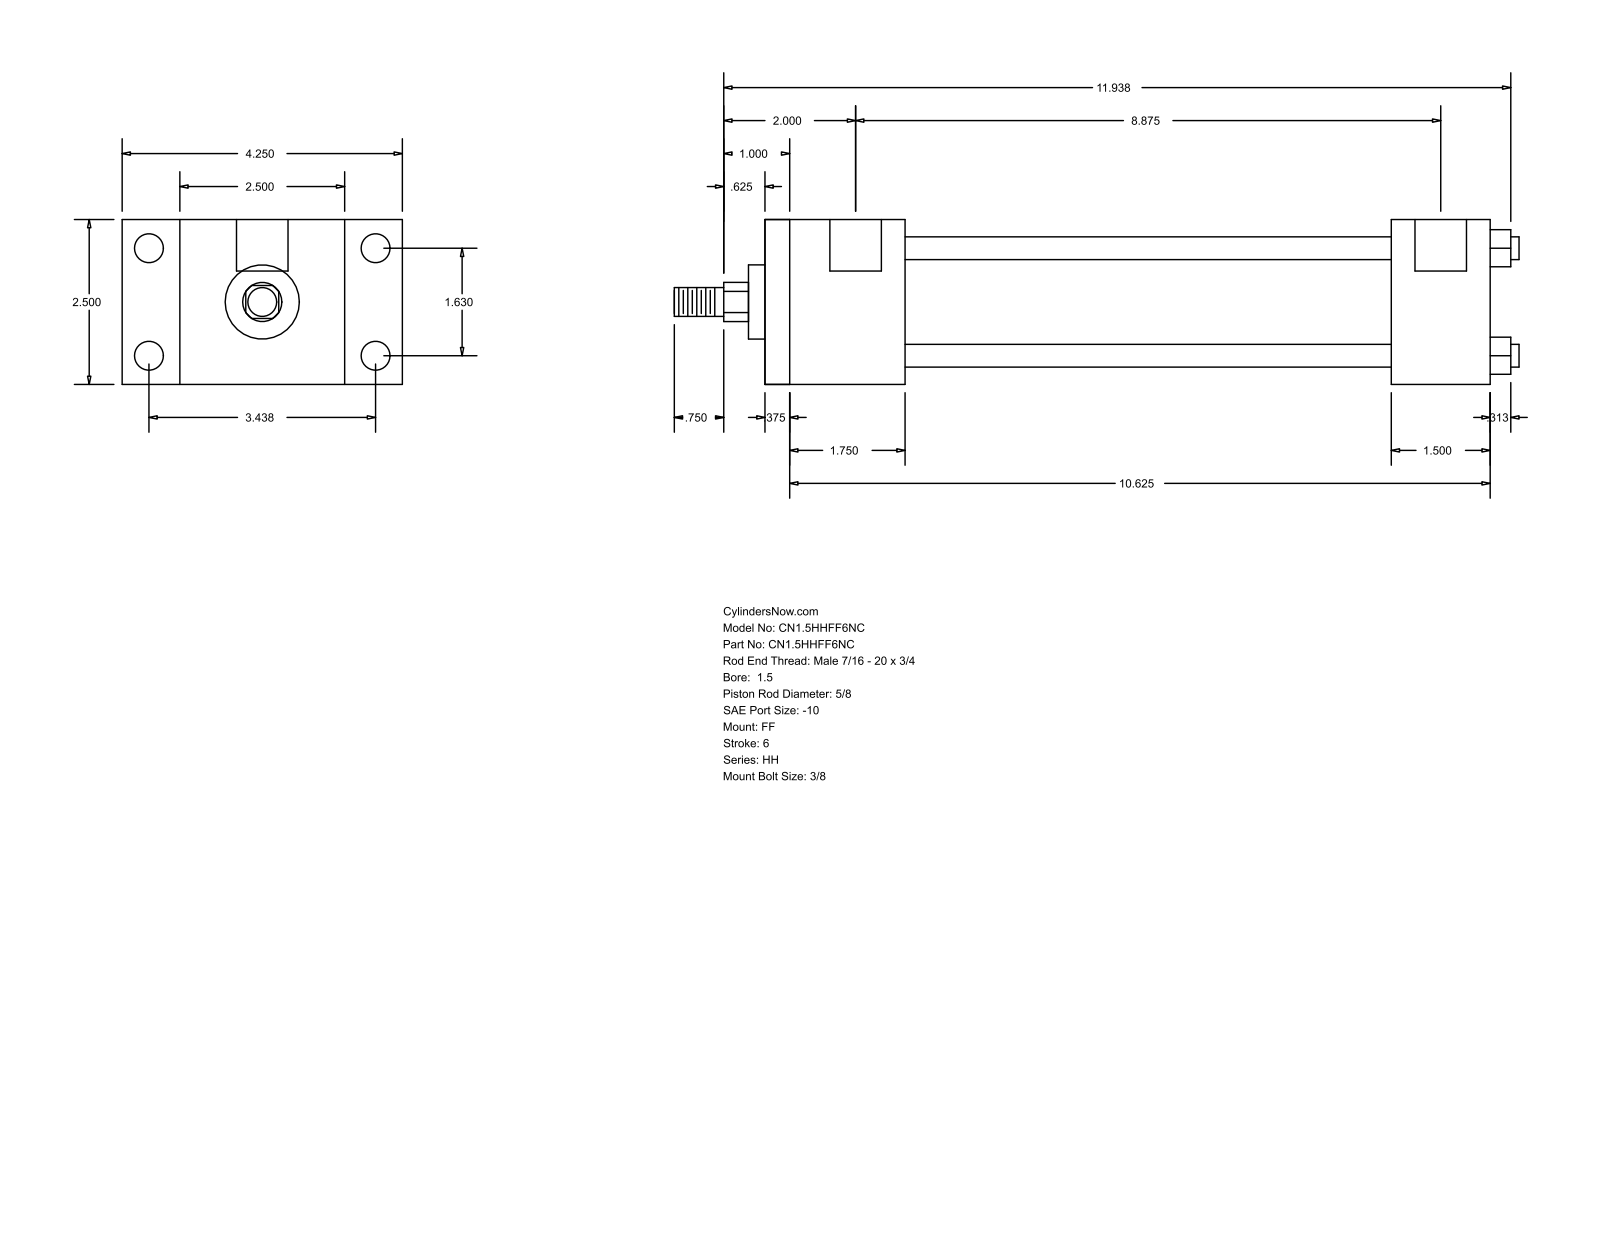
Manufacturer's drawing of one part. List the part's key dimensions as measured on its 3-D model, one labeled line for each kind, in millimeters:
Part name (STEP PRODUCT): HH_FF__0150_0.625
STEP written by: GSSL Pune (CONFIG_CONTROL_DESIGN)
Units: millimetres
Bodies: 0 solids, 92 faces (64 planar, 28 cylindrical, 0 other)
Overall size (bounding box): 325.44 × 107.95 × 63.5
Round holes (diameter × count): ⌀5.56 ×4, ⌀11.13 ×4, ⌀19.84 ×2
Round bosses / shafts (diameter × count): ⌀8.76 ×4, ⌀44.45 ×1, ⌀28.57 ×1, ⌀15.88 ×1, ⌀11.11 ×1
Partial cylindrical surfaces — rounded edges, fillets, slot ends (radius × count): R7.54 ×1
Main face-to-face distances: 63.5, 279.39, 9.52, 269.87, 44.45, 53.97, 225.42, 241.3, 231.78, 187.33
Hole centre spacings: 41.4, 87.32, 96.64, 228.6, 1.58, 1.59, 225.43, 227.01
